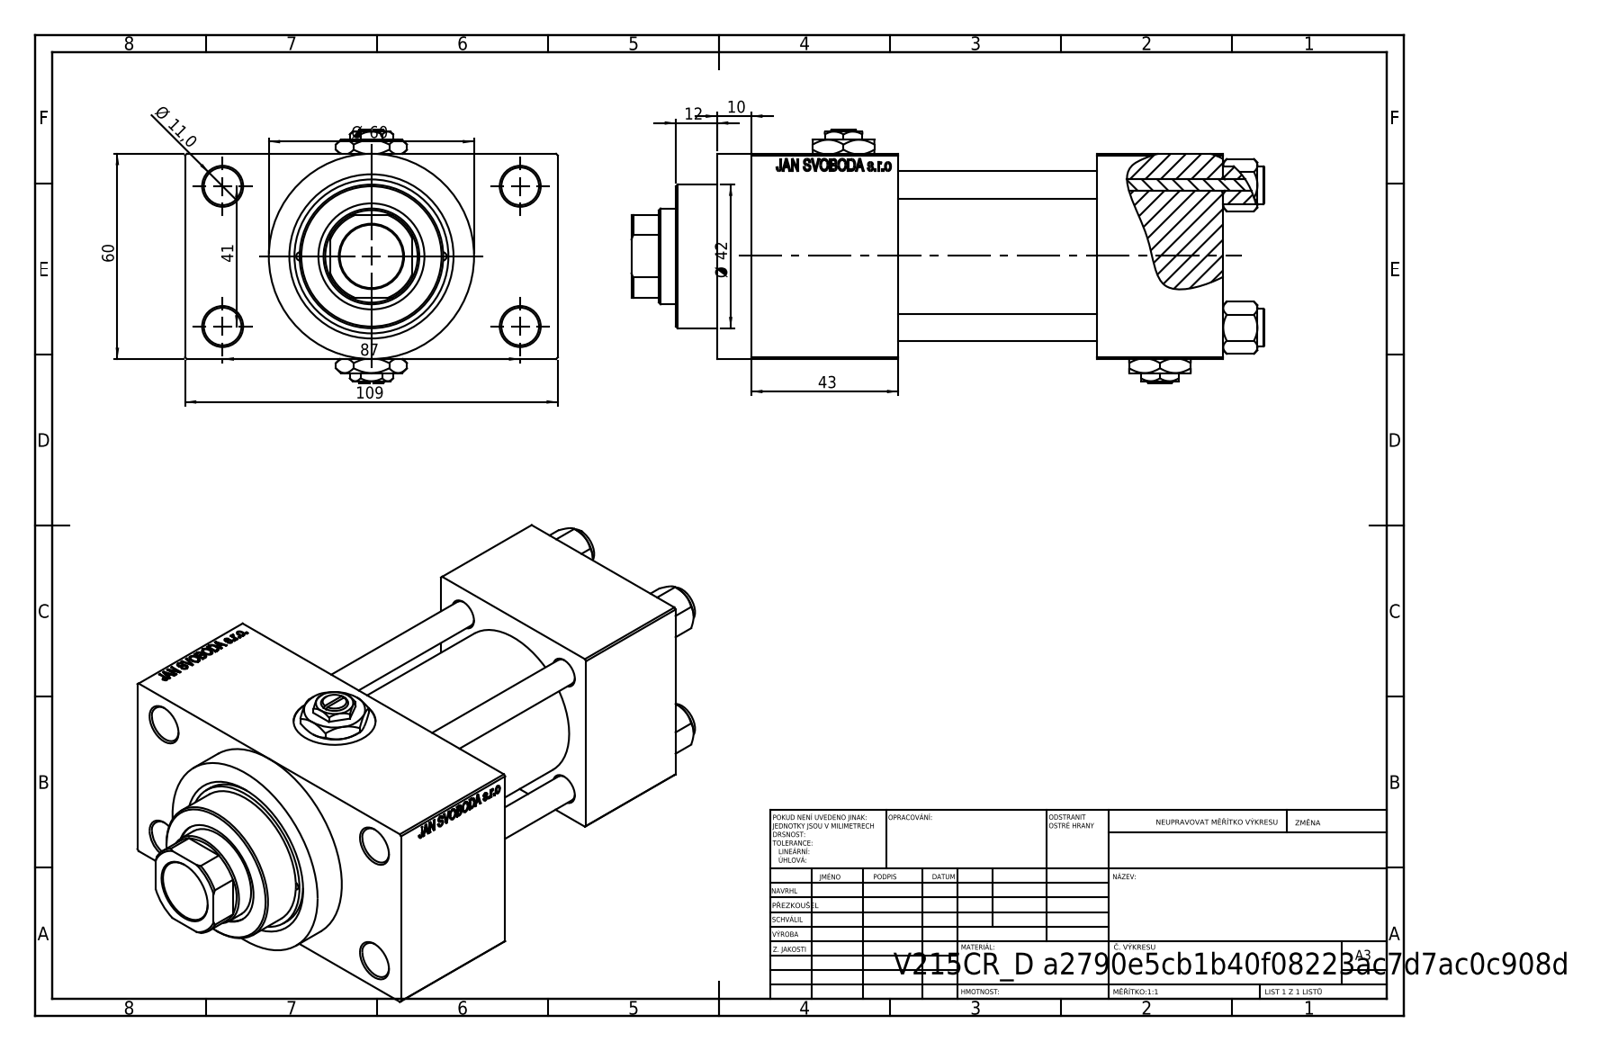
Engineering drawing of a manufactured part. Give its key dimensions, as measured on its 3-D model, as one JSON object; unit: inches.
{"part_name": "V215CR_D_Body; V215CR_VCP_D; V215_VC_A; V215CR_D_TYCINKA (+2 more)", "step_written_by": "SolidWorks 2019 (CONFIG_CONTROL_DESIGN)", "units": "inches", "bodies": {"solids": 13, "faces": 1199, "planar": 546, "cylindrical": 93, "other": 560}, "overall_size": [7.283, 4.291, 2.913], "volume_in3": 32.76, "surface_area_in2": 200.9, "round_holes": [[0.315, 4], [0.433, 4], [0.098, 2], [0.276, 2], [0.656, 2], [0.945, 2], [0.728, 1], [1.102, 1], [1.22, 1], [1.575, 1], [1.772, 1]], "round_bosses_or_shafts": [[0.433, 4], [2.362, 1], [1.811, 1], [1.654, 1]], "partial_cylinders_radius": [[0.531, 1]], "face_to_face_distances": [2.362, 3.327, 0.965, 2.283, 1.457, 3.74, 5.433, 3.976, 1.693, 4.291], "hole_center_spacings": [0.821, 0.892, 1.161, 1.206, 1.642, 1.832, 1.856, 1.893]}
